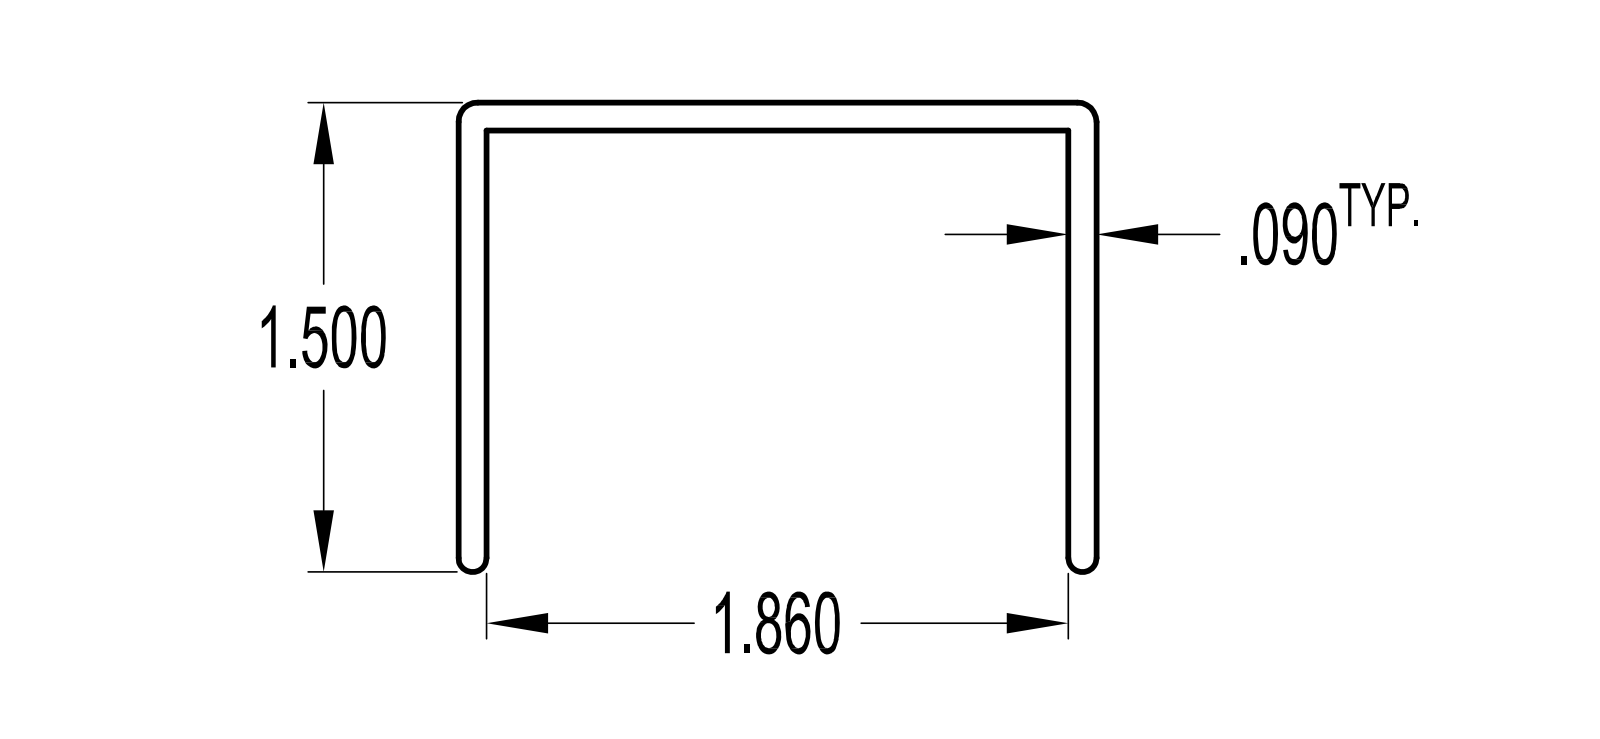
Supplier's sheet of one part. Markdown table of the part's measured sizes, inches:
| quantity | value |
| --- | --- |
| STEP written by | KeyCreator Pro (AUTOMOTIVE_DESIGN) |
| units | inches |
| bodies | 1 solid, 12 faces (8 planar, 4 cylindrical, 0 other) |
| overall size | 6 × 2.04 × 1.5 |
| volume | 2.604 in³ |
| surface area | 59.49 in² |
| partial cylindrical surfaces (radius × count) | 0.045 × 2, 0.062 × 2 |
| main face-to-face distances | 0.09, 1.95, 2.04, 1.86, 6 |
